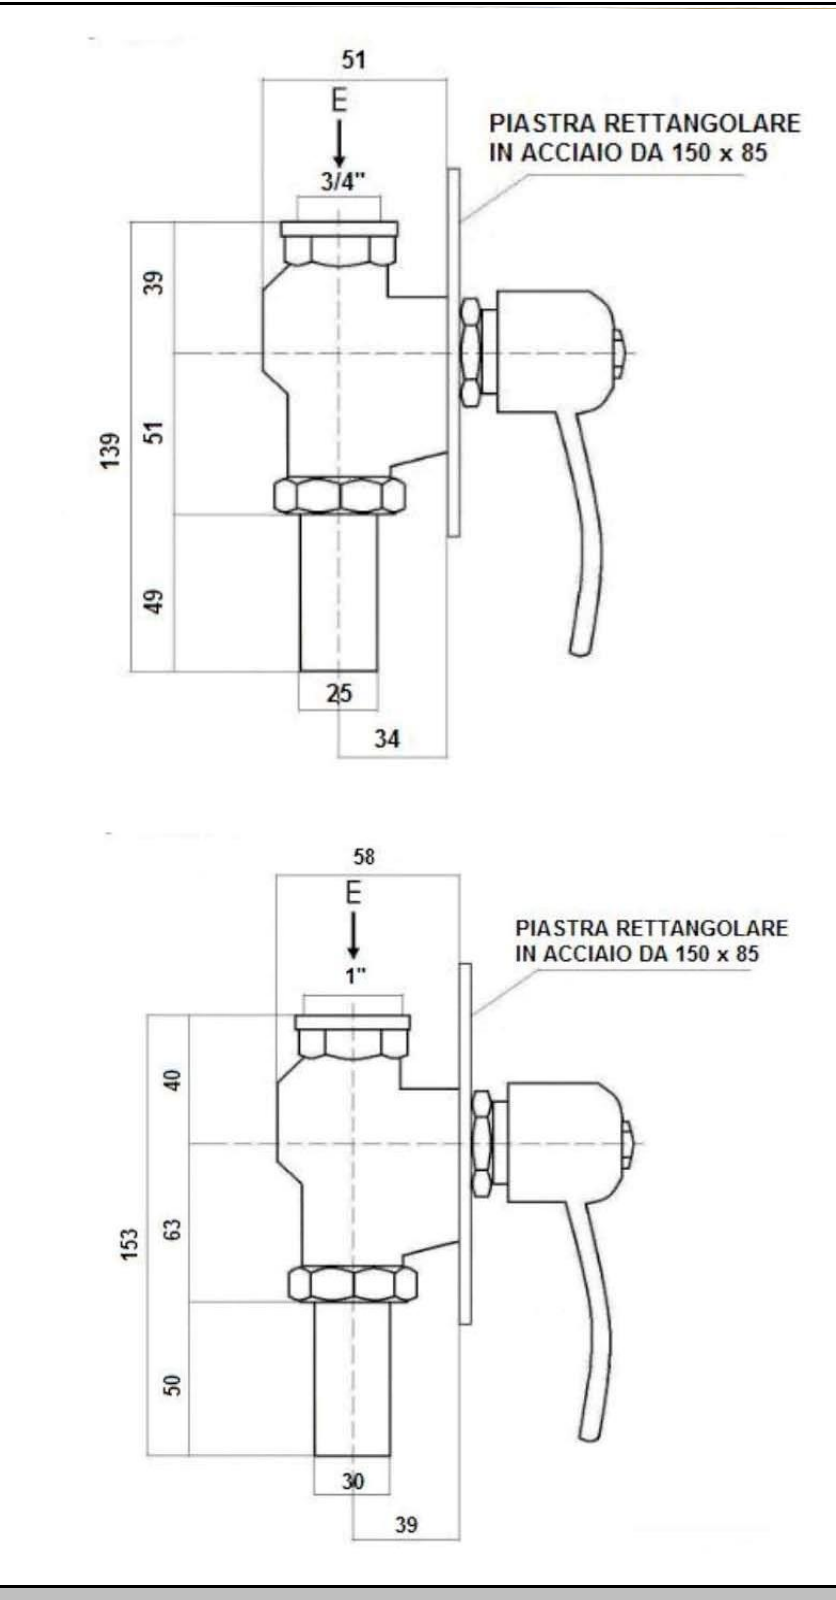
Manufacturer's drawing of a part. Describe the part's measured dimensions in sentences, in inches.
The part is named "4111062CR_A; 4111062CR_B; 4111062CR_C; 4111062CR_D (+8 more)". Its 3-D file was written by "CREO PARAMETRIC BY PTC INC, 2020044 (CONFIG_CONTROL_DESIGN)". It is 12 solids with 643 faces: 291 planar, 210 cylindrical and 142 other. Overall it measures 6.961 by 5.185 by 3.406 inches. Its volume is 9.028 cubic inches and its surface area 179.6 square inches. Round holes: 2 of diameter 1.102, 1 of diameter 0.197, 1 of diameter 0.535, 1 of diameter 0.551, 1 of diameter 0.787, 1 of diameter 0.886, 1 of diameter 0.906, 1 of diameter 0.972, 1 of diameter 0.984, 1 of diameter 1.063, 1 of diameter 1.094, 1 of diameter 1.122. Round bosses or shafts: 2 of diameter 1.378, 2 of diameter 1.02, 1 of diameter 1.673, 1 of diameter 1.476, 1 of diameter 1.437, 1 of diameter 1.398, 1 of diameter 1.339, 1 of diameter 1.181. Partial cylindrical surfaces (rounded edges, fillets, slot ends): 12 of radius 0.197, 11 of radius 0.039, 6 of radius 0.079, 4 of radius 0.118, 4 of radius 0.787, 2 of radius 0.02, 2 of radius 0.276, 1 of radius 0.177. The main face-to-face distances are 0.02, 0.118, 1.093, 1.181, 0.03, 1.083, 1.063, 2.205, 1.211, 2.185.
